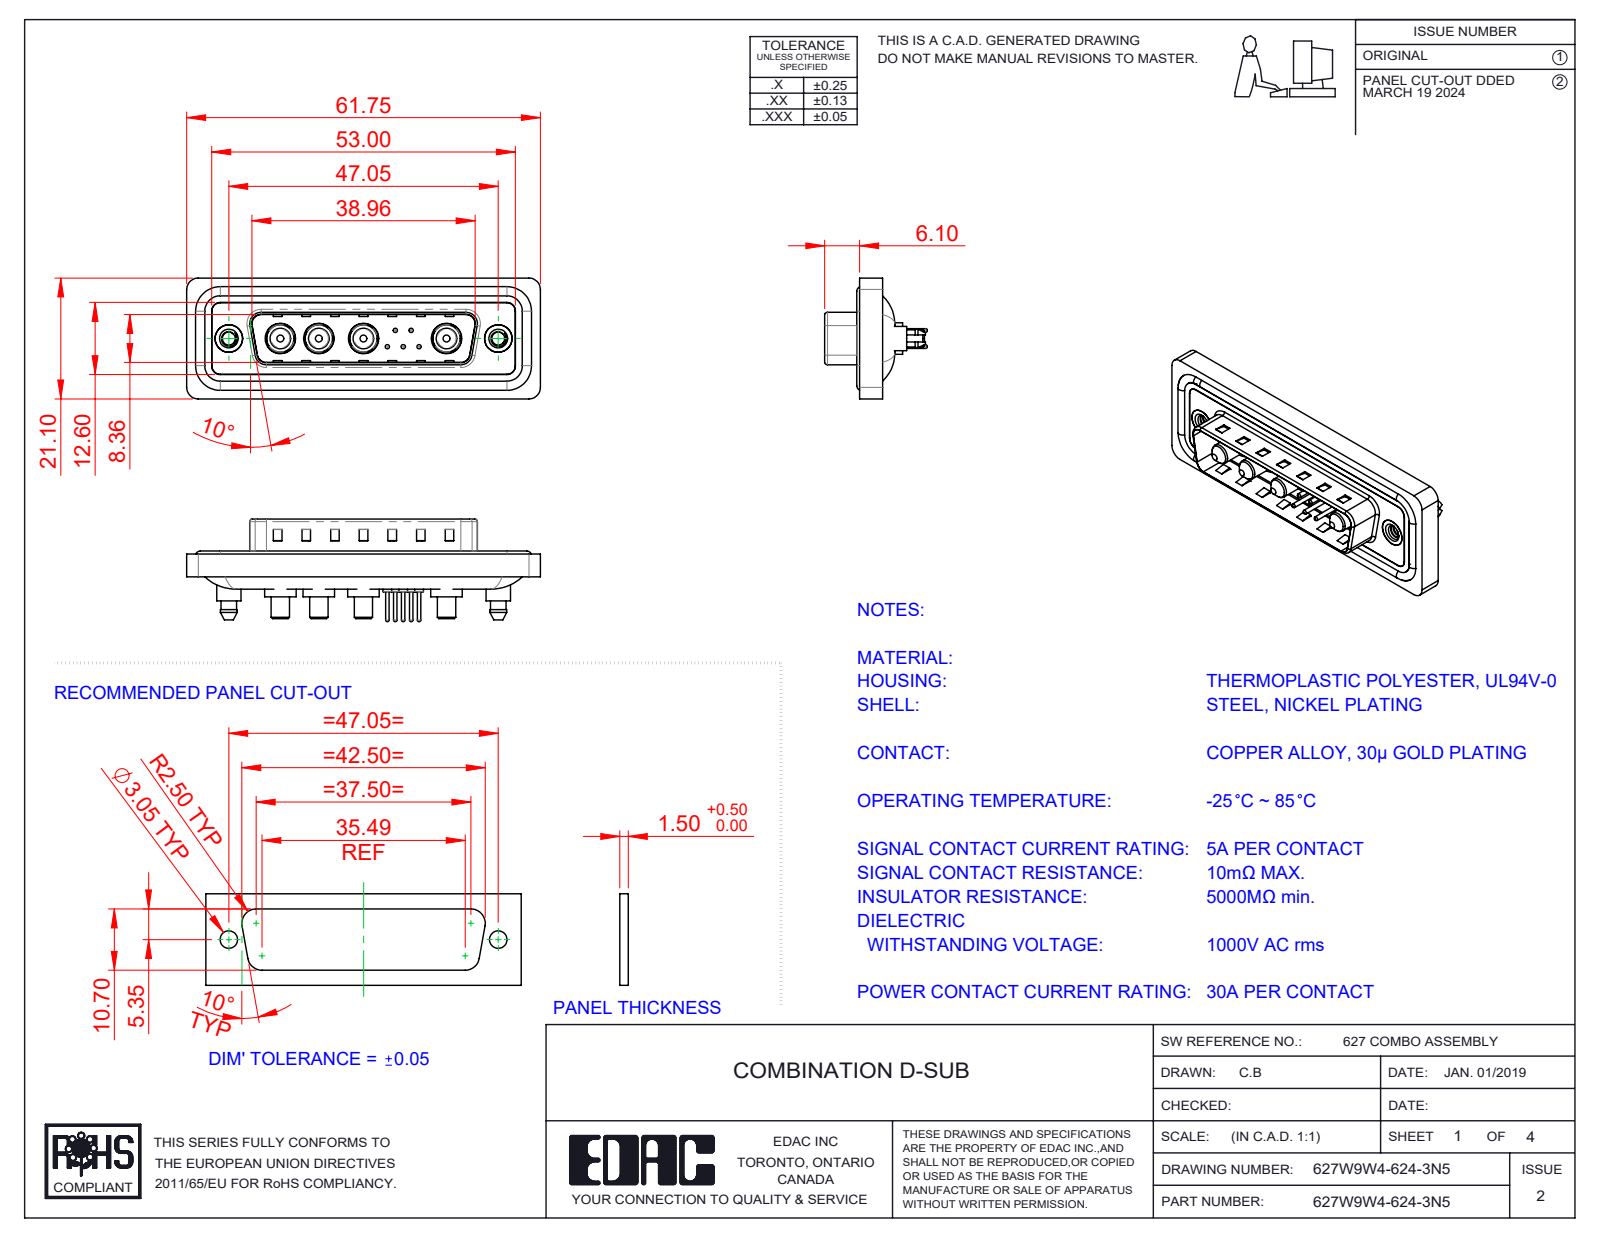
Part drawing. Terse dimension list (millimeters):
name: 627W9W4-624-3N5; 627Combo Threaded Boardlock_5; 627Combo Shell Rear_25 Contacts; 627Combo Housing_9W4 (+5 more)
written by: SolidWorks 2023 (CONFIG_CONTROL_DESIGN)
unit: mm
bodies: 20 solids, 874 faces (300 planar, 366 cylindrical, 208 other)
size: 61.75 × 21.1 × 17.9
volume: 7 566 mm³; area: 12 187 mm²
holes: 5× ⌀0.75, 5× ⌀1.6, 5× ⌀2, 4× ⌀4.85, 4× ⌀5.3, 2× ⌀2.26, 2× ⌀4, 2× ⌀4.8, 2× ⌀5
bosses: 5× ⌀1.5, 5× ⌀0.6, 4× ⌀5.5, 4× ⌀5.2, 4× ⌀4.75, 4× ⌀3.75, 4× ⌀3.6, 4× ⌀3.2
rounds: 24× R1.5, 18× R2, 10× R1.6, 8× R0.5, 4× R0.25, 4× R0.6, 4× R0.65, 4× R0.9
face distances: 0.4, 1.5, 1.1, 0.5, 3.1, 1.6, 2.9, 0.82, 9.58, 5.65
hole spacings: 3.16, 2.77, 5.04, 14.51, 2.78, 4.4, 4.41, 5
